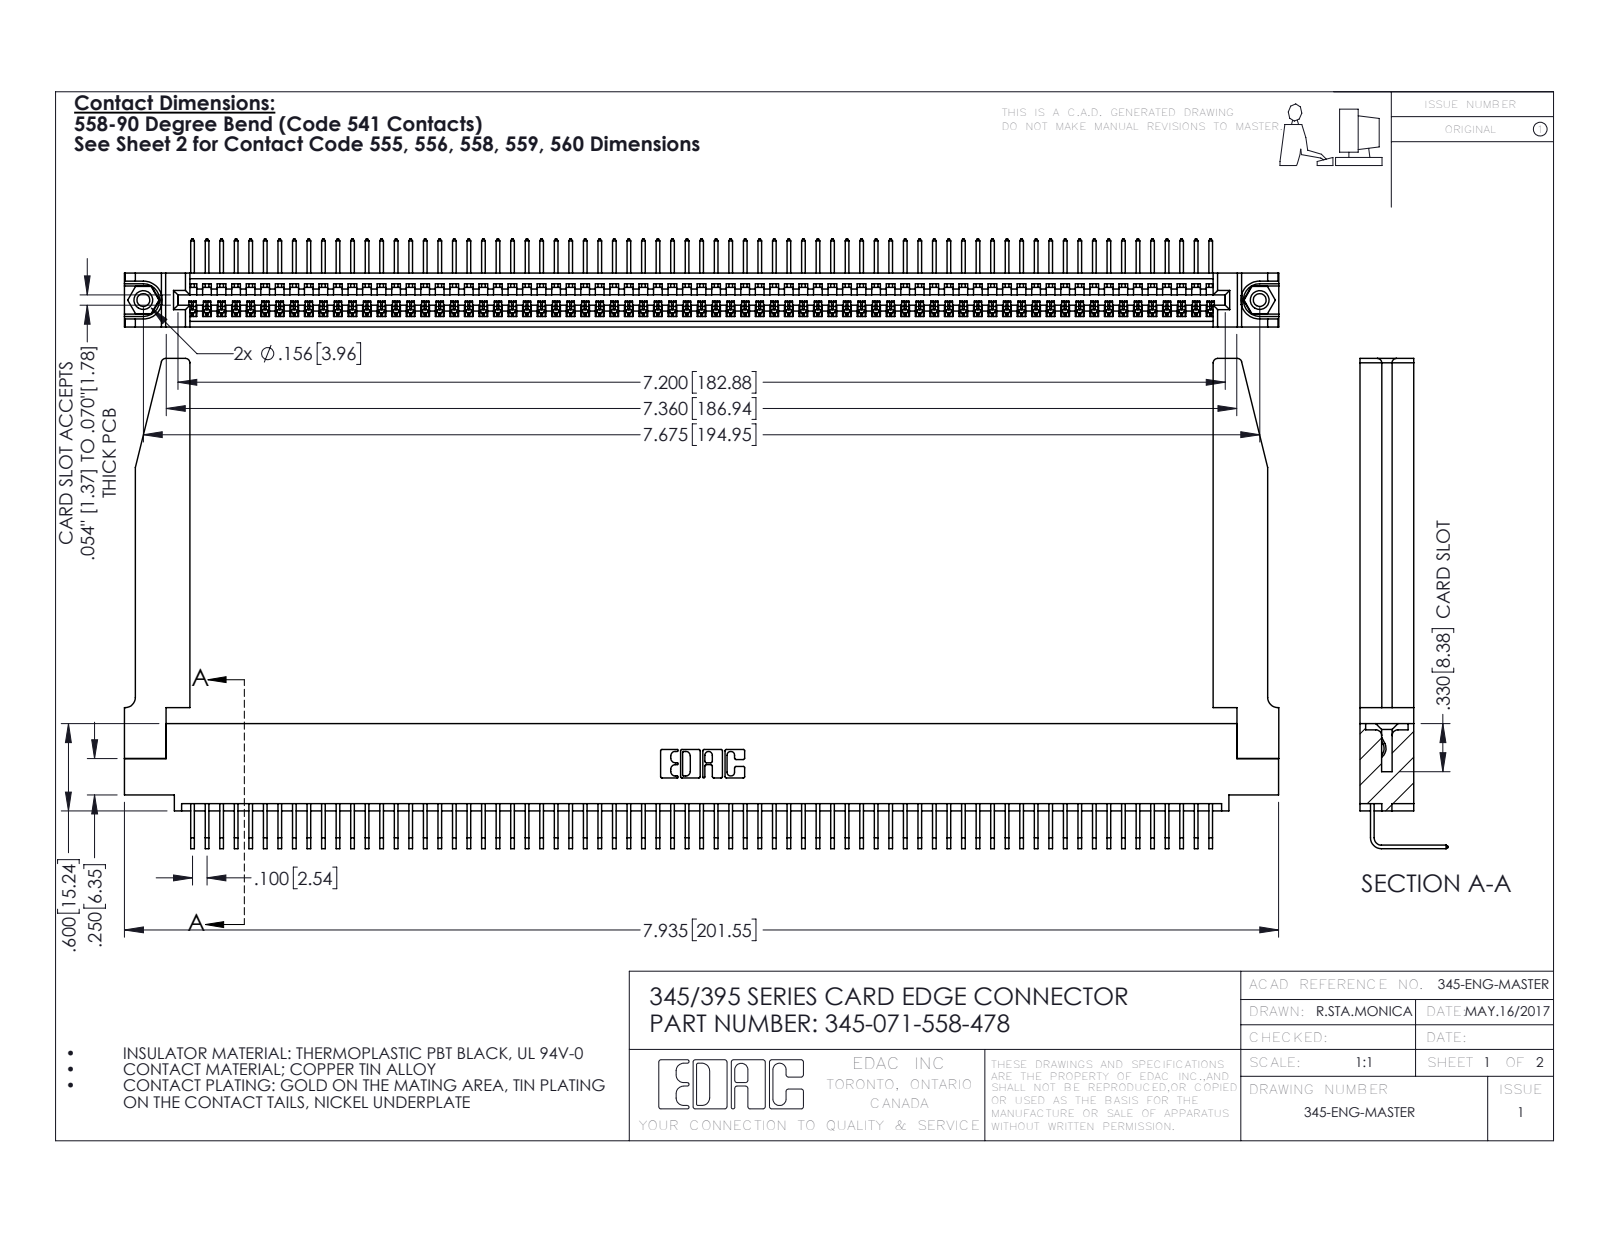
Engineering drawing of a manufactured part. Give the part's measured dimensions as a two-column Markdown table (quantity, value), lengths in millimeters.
| quantity | value |
| --- | --- |
| part name | 345-071-558-478; 345 Part_0.110 Offset - 0.156 Dia-TH; 345-220-078_345-220-078; 345-250-001_345-250-001-102 (+1 more) |
| STEP written by | SolidWorks 2016 (CONFIG_CONTROL_DESIGN) |
| units | millimeters |
| bodies | 76 solids, 4624 faces (3208 planar, 1364 cylindrical, 52 other) |
| overall size | 201.6 × 85.6 × 15.4 |
| volume | 27 320 mm³ |
| surface area | 34 690 mm² |
| round holes (diameter × count) | 2.3 × 2, 3.2 × 2, 4 × 2, 1.6 × 1 |
| round bosses / shafts (diameter × count) | 3.9 × 2 |
| partial cylindrical surfaces (radius × count) | 0.2 × 142, 0.3 × 22, 0.8 × 8, 0.2 × 6, 0.8 × 6, 0.7 × 3, 0.8 × 2, 1 × 2 |
| main face-to-face distances | 1.8, 9.4, 7.6, 2.5, 6.9, 0.6, 5.1, 5.7, 3.8, 3.8 |
| hole center spacings | 6.9, 189, 194.9 |
